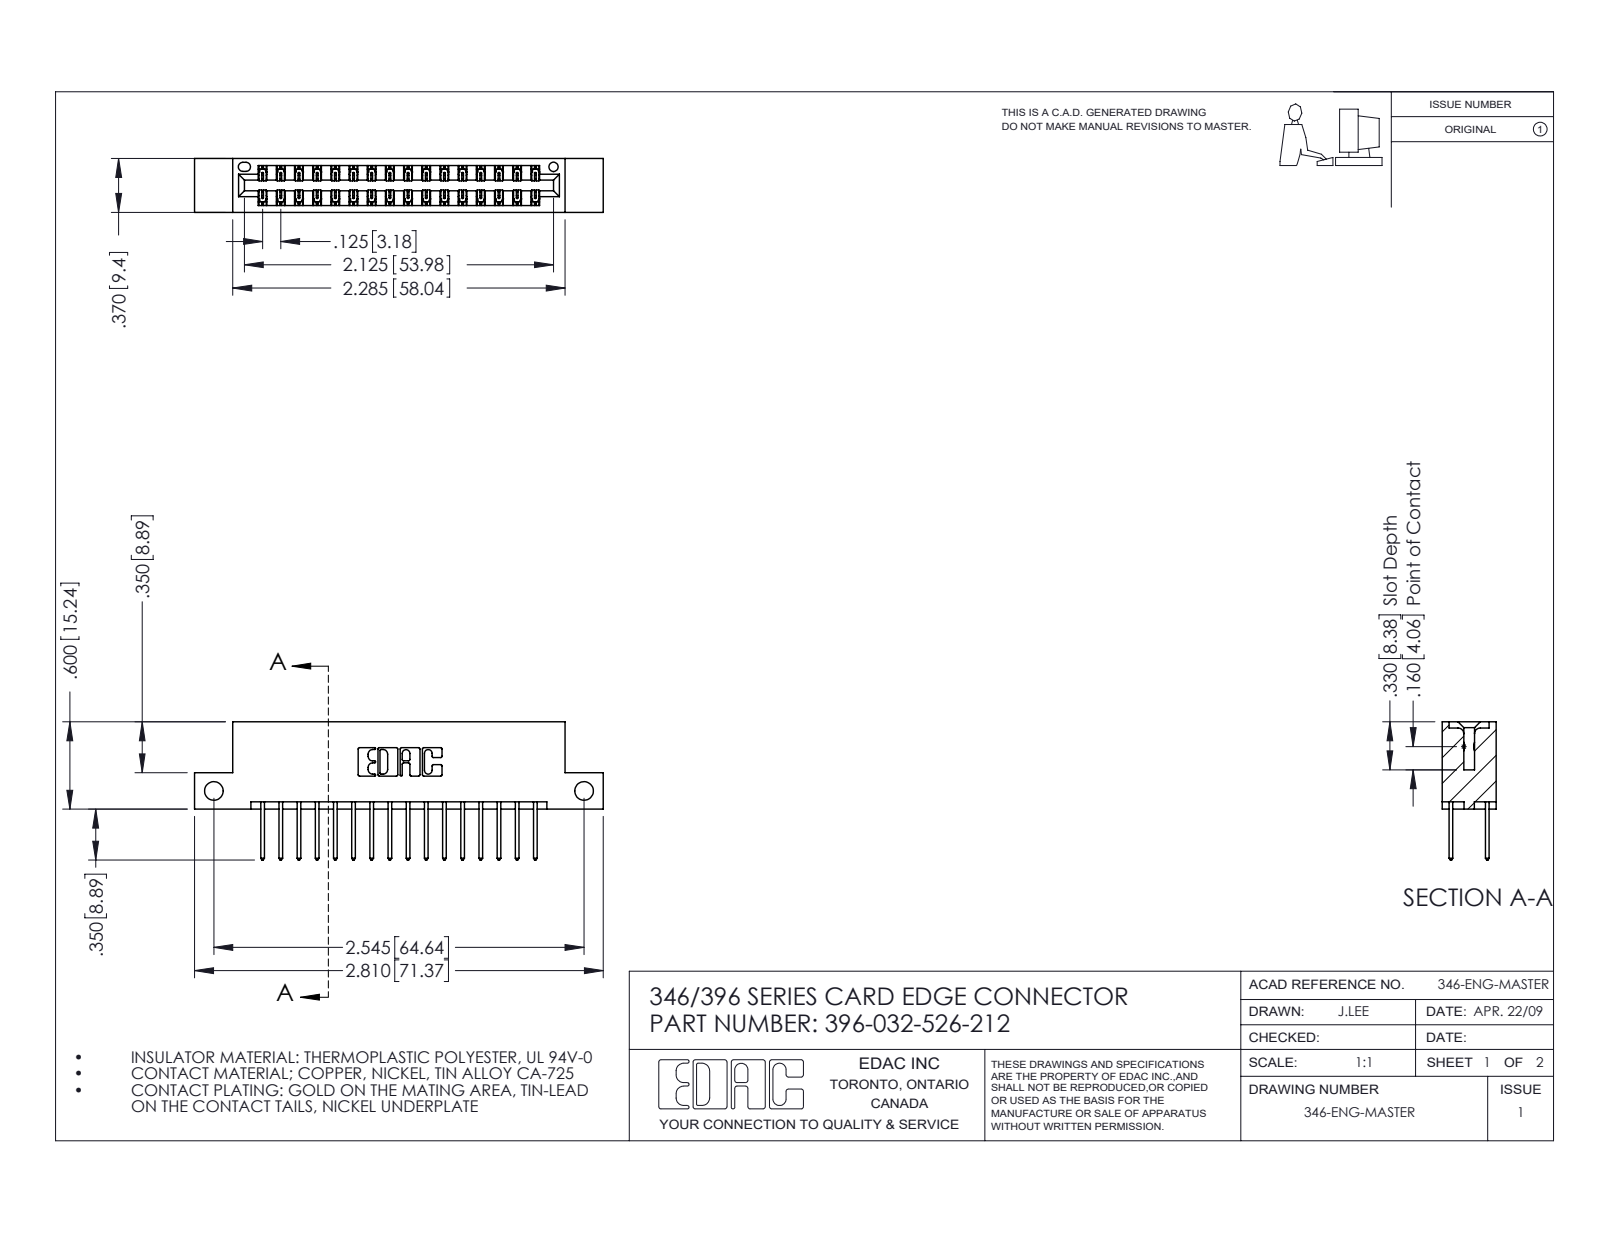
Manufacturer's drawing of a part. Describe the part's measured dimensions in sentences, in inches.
The part is named "346 Part_Flush Mounting Lugs - Side Mount; 345-292-001_345-293-126; 396-032-526-212". Its 3-D file was written by "SolidWorks 2016 (CONFIG_CONTROL_DESIGN)". It is 33 solids with 1786 faces: 1196 planar, 590 cylindrical and 0 other. Overall it measures 2.81 by 0.95 by 0.37 inches. Its volume is 0.41 cubic inches and its surface area 13.84 square inches. Round holes: 2 of diameter 0.128, 1 of diameter 0.064. Partial cylindrical surfaces (rounded edges, fillets, slot ends): 48 of radius 0.006, 32 of radius 0.01, 22 of radius 0.01, 6 of radius 0.007, 6 of radius 0.031, 3 of radius 0.026, 2 of radius 0.014, 2 of radius 0.022. The main face-to-face distances are 0.048, 0.322, 0.25, 0.37, 0.072, 0.298, 0.025, 0.275, 0.148, 0.222. The hole center spacings are 2.545.
